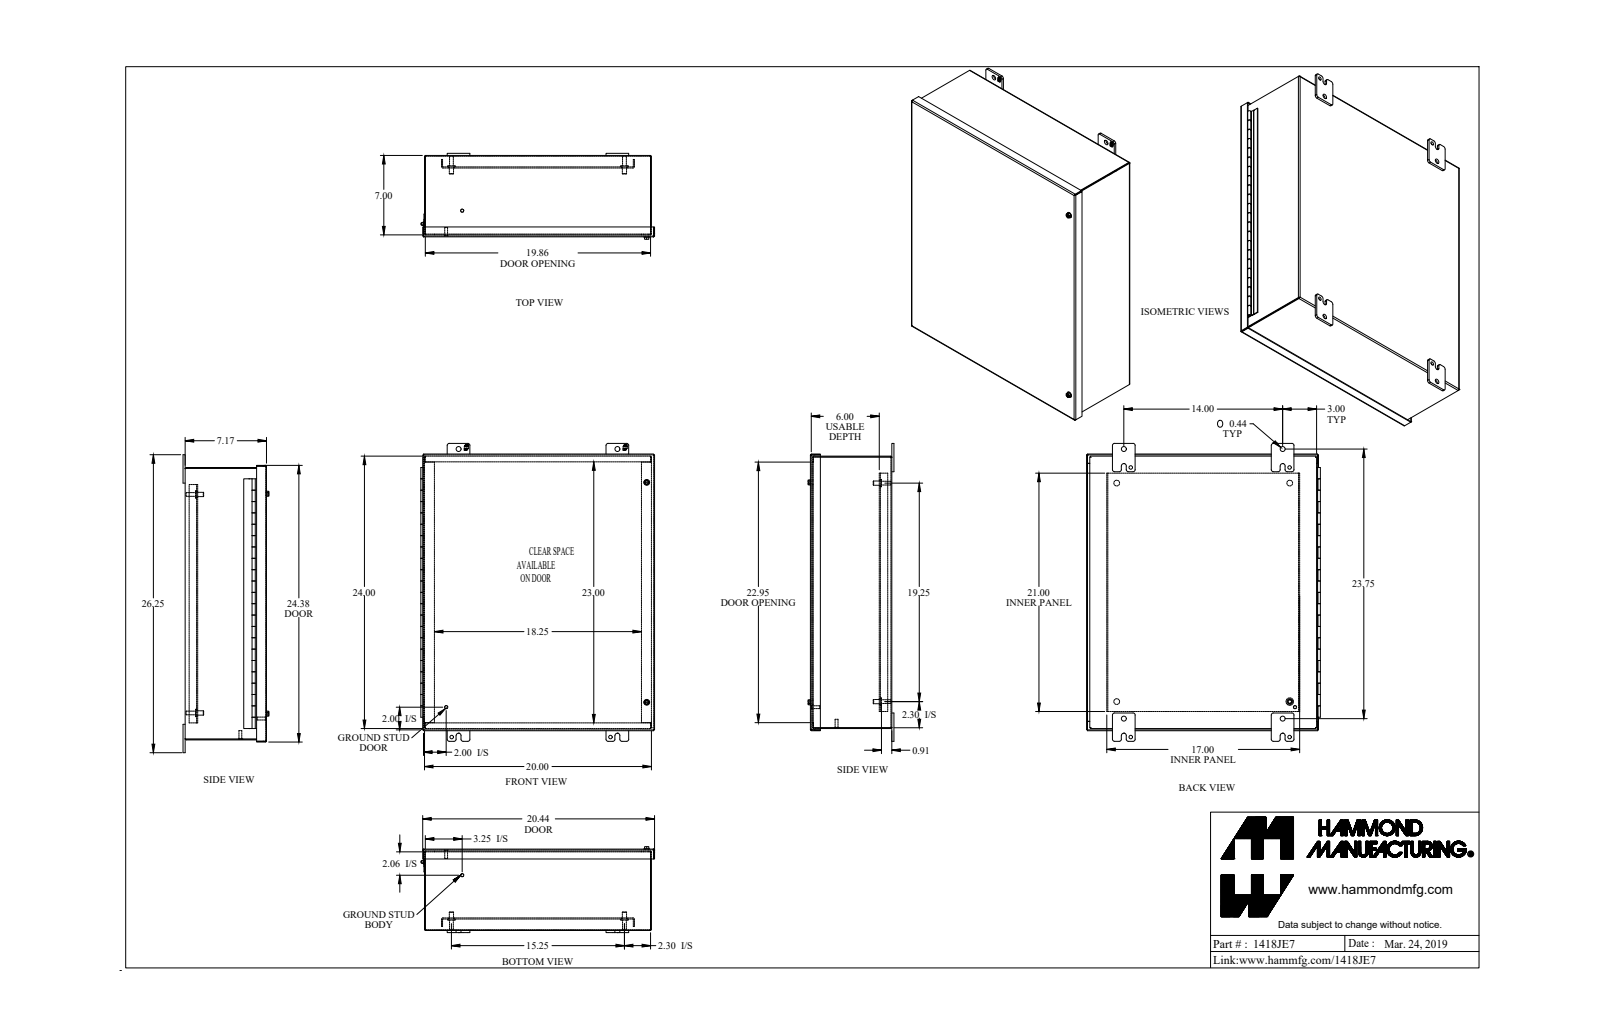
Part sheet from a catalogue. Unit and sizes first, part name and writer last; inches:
Units: inches
Overall size (bounding box): 26.25 × 20.604 × 7.571
Round holes (diameter × count): ⌀0.313 ×6, ⌀0.437 ×4, ⌀0.5 ×4, ⌀0.26 ×2, ⌀0.266 ×2, ⌀0.28 ×2, ⌀0.29 ×2, ⌀0.307 ×2, ⌀0.397 ×2, ⌀0.445 ×2, ⌀0.187 ×1, ⌀3.5 ×1
Round bosses / shafts (diameter × count): ⌀0.65 ×4, ⌀0.375 ×4, ⌀0.33 ×4, ⌀1 ×2, ⌀0.51 ×2, ⌀0.5 ×2, ⌀0.39 ×2, ⌀0.281 ×2
Partial cylindrical surfaces — rounded edges, fillets, slot ends (radius × count): R0.188 ×24, R0.25 ×20, R0.036 ×12, R0.108 ×12, R0.218 ×8, R0.133 ×6, R0.06 ×5, R0.125 ×4
Main face-to-face distances: 0.072, 7.1, 7.172, 7.028, 0.095, 5.996, 6.091, 1.104, 1.032, 6.068
Hole centre spacings: 24.559, 12.279, 14, 15.25, 1.907, 1.966, 3.065, 12.28
Volume: 190 in³ · Surface area: 4 668 in²
Bodies: 32 solids, 942 faces (587 planar, 313 cylindrical, 42 other)
Part name (STEP PRODUCT): 1418JE7_Default
STEP written by: SolidWorks 2018 (CONFIG_CONTROL_DESIGN)
